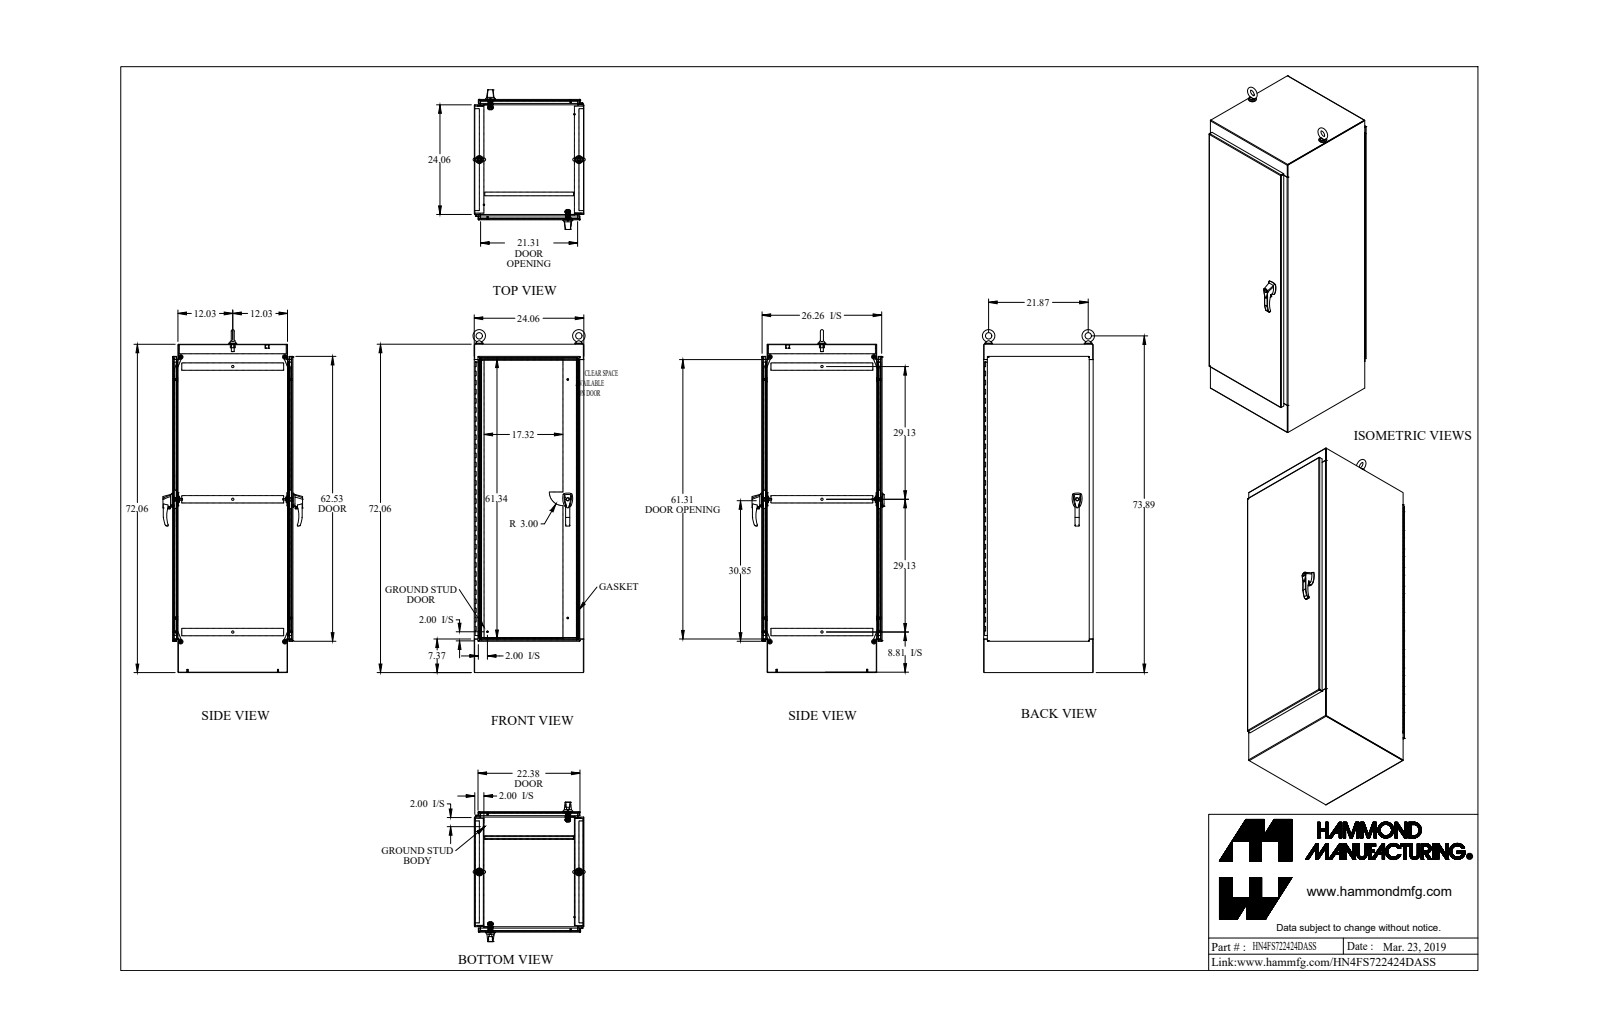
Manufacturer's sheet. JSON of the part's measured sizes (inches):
{"part_name": "HN4FS722424DASS", "step_written_by": "SolidWorks 2018 (AUTOMOTIVE_DESIGN)", "units": "inches", "bodies": {"solids": 84, "faces": 3176, "planar": 1425, "cylindrical": 1483, "other": 268}, "overall_size": [75.256, 30.664, 24.604], "volume_in3": 1035, "surface_area_in2": 21779, "round_holes": [[0.304, 20], [0.35, 8], [0.25, 4], [0.257, 4], [0.28, 4], [0.281, 4], [0.313, 4], [0.39, 4], [0.413, 4], [0.5, 3], [0.11, 2], [0.173, 2]], "round_bosses_or_shafts": [[1, 4], [0.75, 4], [0.63, 4], [0.44, 4], [0.37, 4], [0.313, 4], [0.281, 4], [0.25, 4]], "partial_cylinders_radius": [[0.125, 44], [0.043, 42], [0.138, 36], [0.017, 32], [0.048, 26], [0.143, 26], [0.5, 26], [0.06, 21]], "face_to_face_distances": [0.095, 23.965, 26.339, 23.87, 24.06, 25.152, 1.187, 26.244, 26.434, 71.965], "hole_center_spacings": [6, 23.12, 12, 25.349, 18, 28.68, 24, 32.78]}
